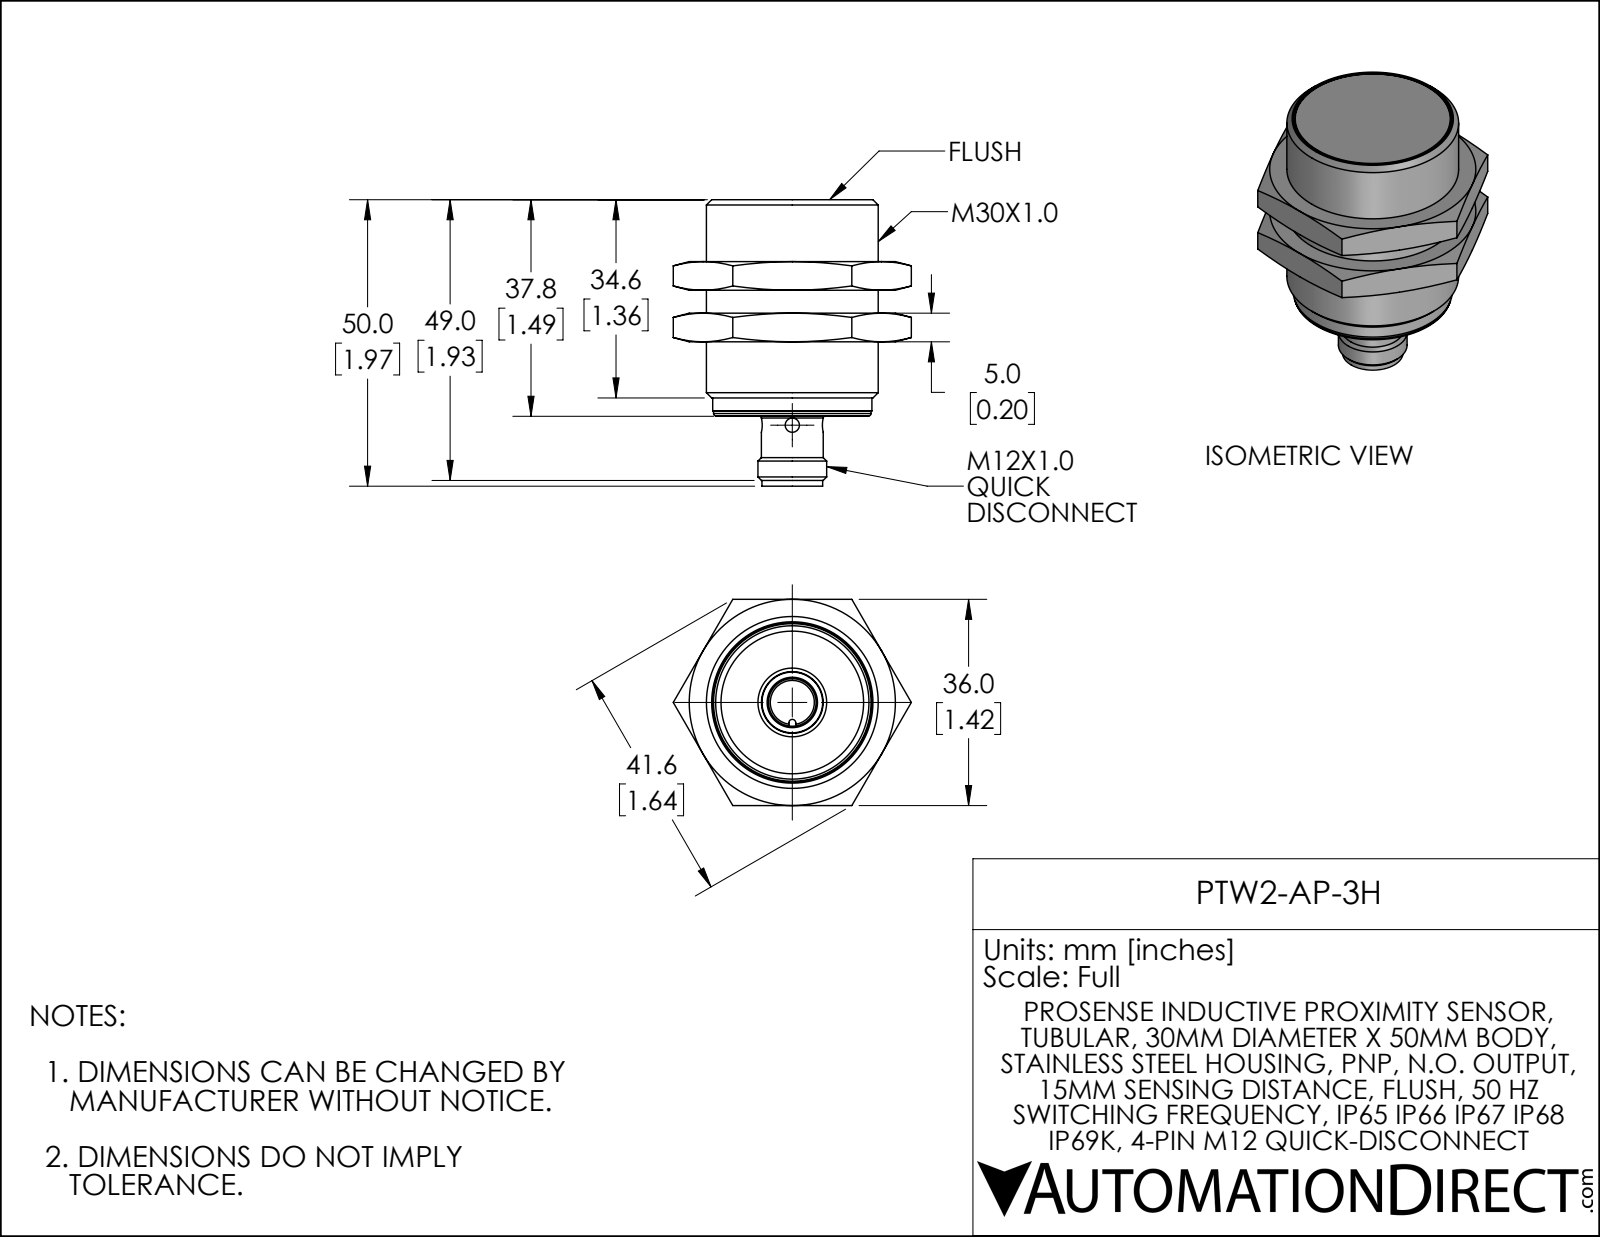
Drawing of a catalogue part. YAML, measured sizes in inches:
part_name: "PTW2-AP-3H"
step_written_by: "SolidWorks 2019 (CONFIG_CONTROL_DESIGN)"
units: inches
bodies: {solids: 3, faces: 86, planar: 27, cylindrical: 20, other: 39}
overall_size: [1.969, 1.637, 1.417]
volume: 1.936
surface_area: 14.65
round_holes:
  - {diameter: 0.098, count: 2}
  - {diameter: 0.327, count: 1}
  - {diameter: 1.089, count: 1}
  - {diameter: 1.117, count: 1}
round_bosses_or_shafts:
  - {diameter: 1.181, count: 1}
  - {diameter: 1.094, count: 1}
  - {diameter: 1.083, count: 1}
  - {diameter: 1.074, count: 1}
  - {diameter: 0.472, count: 1}
  - {diameter: 0.425, count: 1}
  - {diameter: 0.417, count: 1}
partial_cylinders:
  - {radius: 0.024, count: 1}
  - {radius: 0.185, count: 1}
face_to_face_distances: [0.197, 0.78, 1.417, 0.709, 1.488, 0.583, 0.906, 0.512, 0.394, 0.976]
